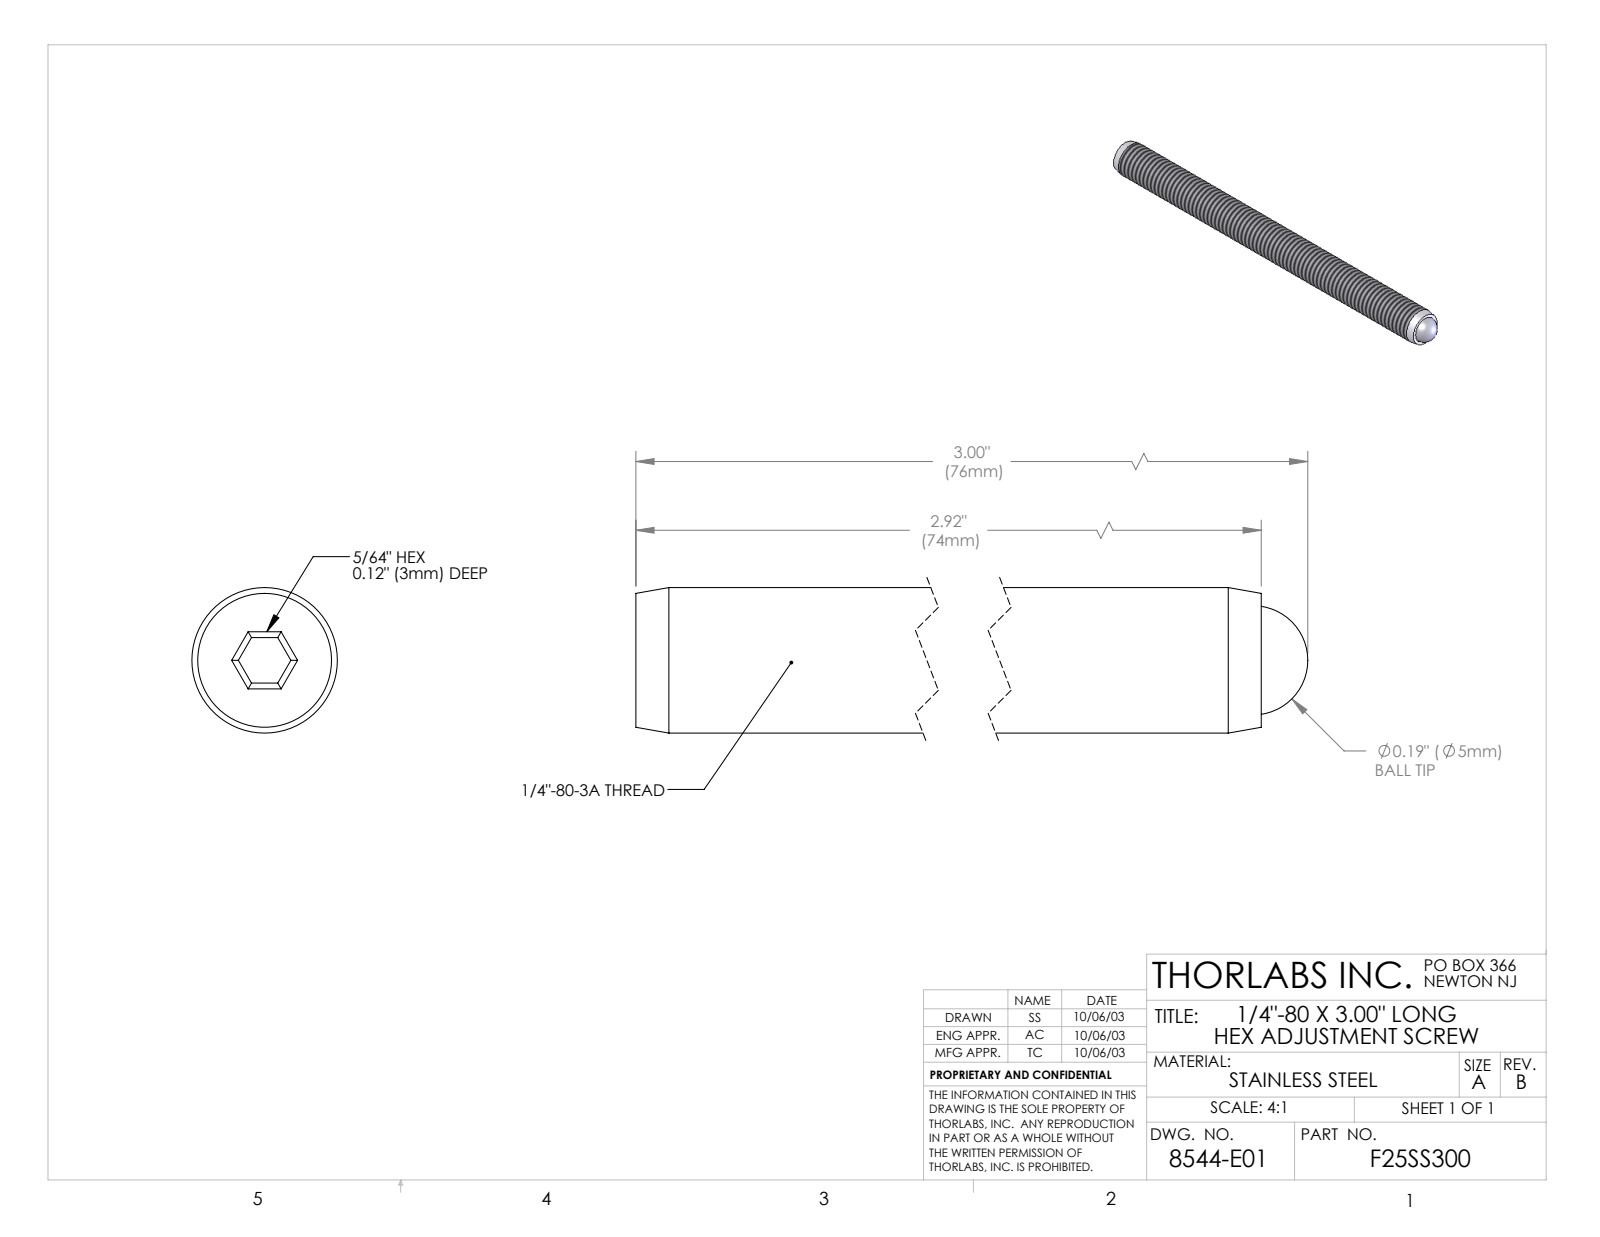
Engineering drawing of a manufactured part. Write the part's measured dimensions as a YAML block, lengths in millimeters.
part_name: "8544-E0W"
step_written_by: "SolidWorks 2007 (AUTOMOTIVE_DESIGN)"
units: millimeters
bodies: {solids: 2, faces: 29, planar: 15, cylindrical: 4, other: 10}
overall_size: [76.2, 6.35, 6.35]
volume: 2350
surface_area: 1650
round_holes:
  - {diameter: 4.78, count: 1}
round_bosses_or_shafts:
  - {diameter: 6.35, count: 1}
face_to_face_distances: [74.17, 1.99, 3.05, 71.12, 1.98]
